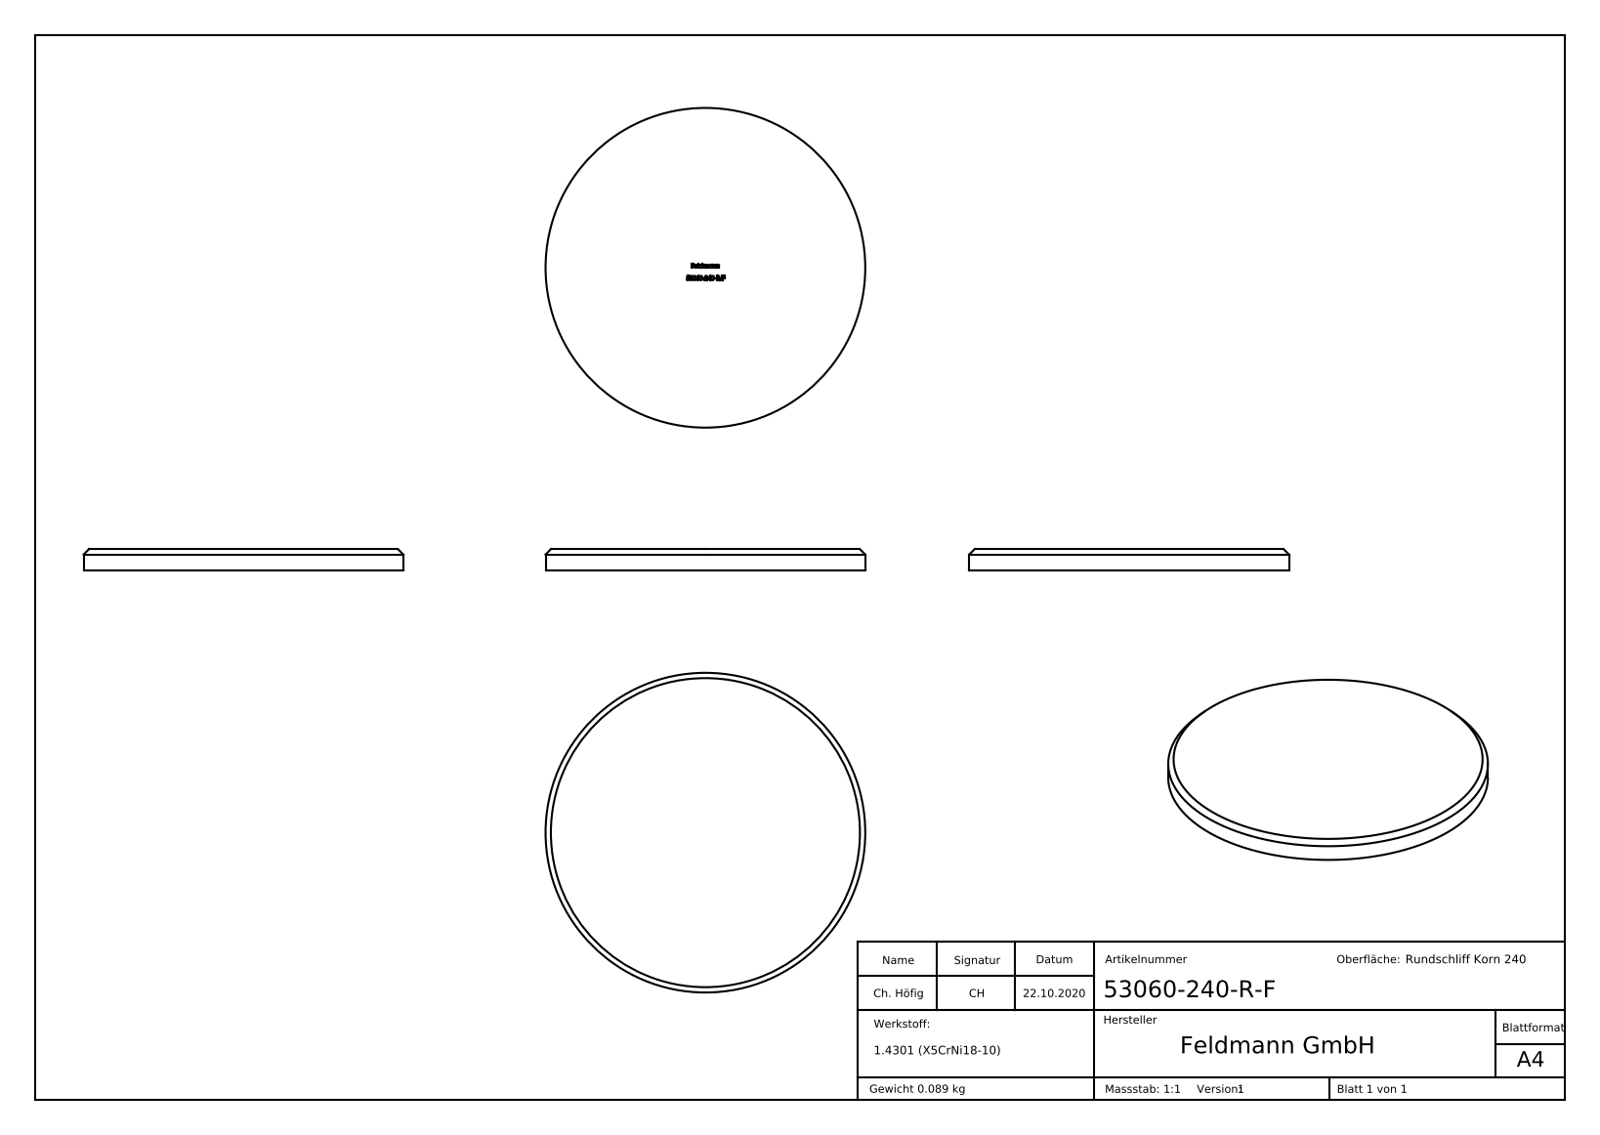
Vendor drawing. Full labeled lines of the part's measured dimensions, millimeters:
Part name (STEP PRODUCT): 53060-240-R-F
STEP written by: SolidWorks 2018 (CONFIG_CONTROL_DESIGN)
Units: millimetres
Bodies: 1 solid, 271 faces (150 planar, 2 cylindrical, 119 other)
Overall size (bounding box): 60 × 60 × 4
Volume: 11 216 mm³ · Surface area: 6 304 mm²
Round bosses / shafts (diameter × count): ⌀60 ×1
Main face-to-face distances: 4, 3.9, 2.32, 1.21, 3.49, 0.79, 1.78, 2.24, 2.2, 0.83
